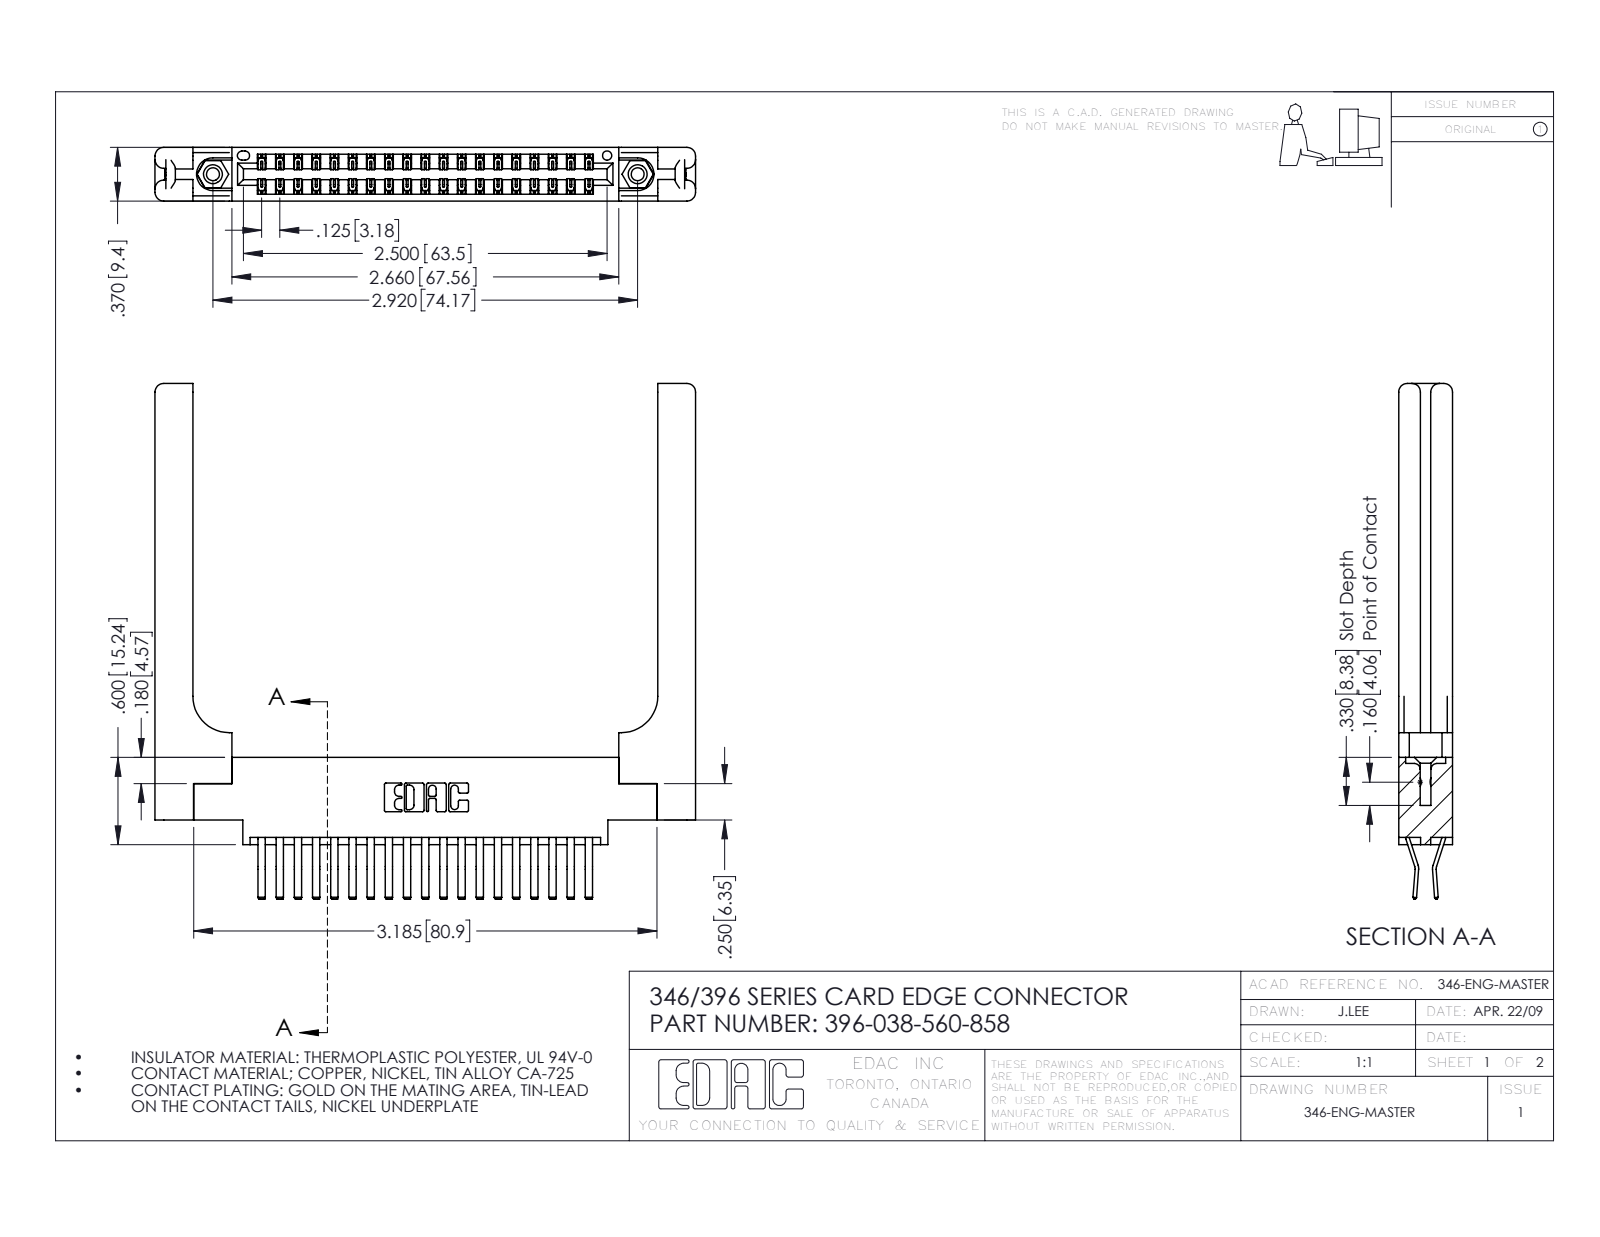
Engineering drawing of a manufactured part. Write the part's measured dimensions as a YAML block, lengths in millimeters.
part_name: "346-220-058_345-220-058; 345-250-001_345-250-001-102; 346 Part_0.170 Offset - 0.156 Dia-TH; 345-292-001_560 Tail (+1 more)"
step_written_by: "SolidWorks 2016 (CONFIG_CONTROL_DESIGN)"
units: millimeters
bodies: {solids: 43, faces: 2434, planar: 1558, cylindrical: 816, other: 60}
overall_size: [94.4, 90, 9.4]
volume: 16620
surface_area: 17990
round_holes:
  - {diameter: 2.3, count: 2}
  - {diameter: 3.2, count: 2}
  - {diameter: 4, count: 2}
  - {diameter: 1.6, count: 1}
round_bosses_or_shafts:
  - {diameter: 3.9, count: 2}
partial_cylinders:
  - {radius: 0.2, count: 57}
  - {radius: 0.3, count: 22}
  - {radius: 1.5, count: 16}
  - {radius: 0.2, count: 6}
  - {radius: 0.8, count: 6}
  - {radius: 0.7, count: 3}
  - {radius: 0.3, count: 2}
  - {radius: 0.4, count: 2}
face_to_face_distances: [9.4, 1.8, 3.8, 3.8, 1.2, 8.2, 0.6, 6.4, 2, 2.6]
hole_center_spacings: [6.2, 68.9, 74.2]
